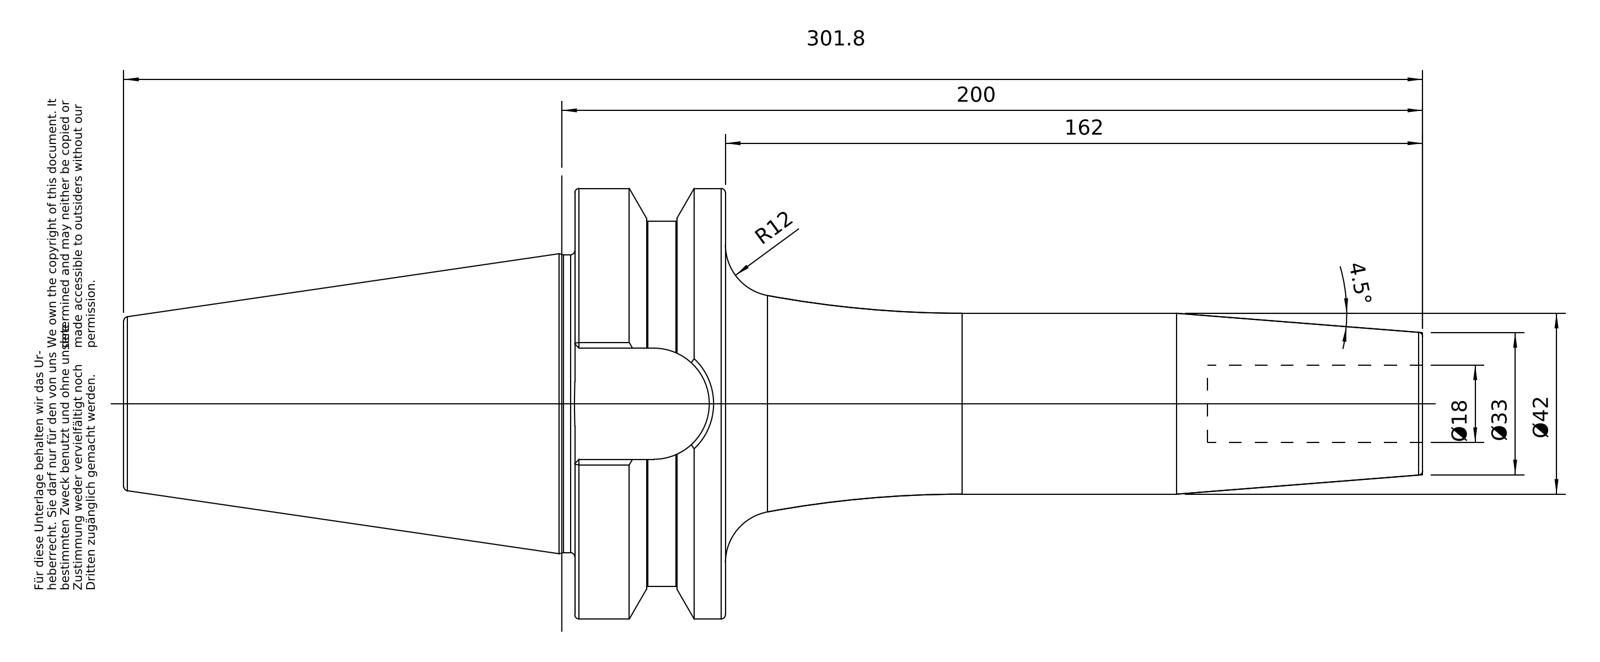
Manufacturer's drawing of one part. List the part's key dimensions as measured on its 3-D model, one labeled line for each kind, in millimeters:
Part name (STEP PRODUCT): 50-646-18
STEP written by: PRO/ENGINEER BY PARAMETRIC TECHNOLOGY CORPORATION, 2010430 (CONFIG_CONTROL_DESIGN)
Units: millimetres
Bodies: 1 solid, 98 faces (26 planar, 22 cylindrical, 50 other)
Overall size (bounding box): 301.8 × 99.97 × 99.97
Volume: 683 499 mm³ · Surface area: 74 052 mm²
Round holes (diameter × count): ⌀18 ×1, ⌀20.75 ×1, ⌀25.02 ×1, ⌀25.7 ×1
Round bosses / shafts (diameter × count): ⌀99.97 ×1, ⌀84.75 ×1, ⌀69.15 ×1, ⌀42 ×1, ⌀24.01 ×1
Partial cylindrical surfaces — rounded edges, fillets, slot ends (radius × count): R12.9 ×1
Main face-to-face distances: 35, 70.4, 197, 162, 104.8, 139.8, 301.8, 25.8, 251.8, 147
